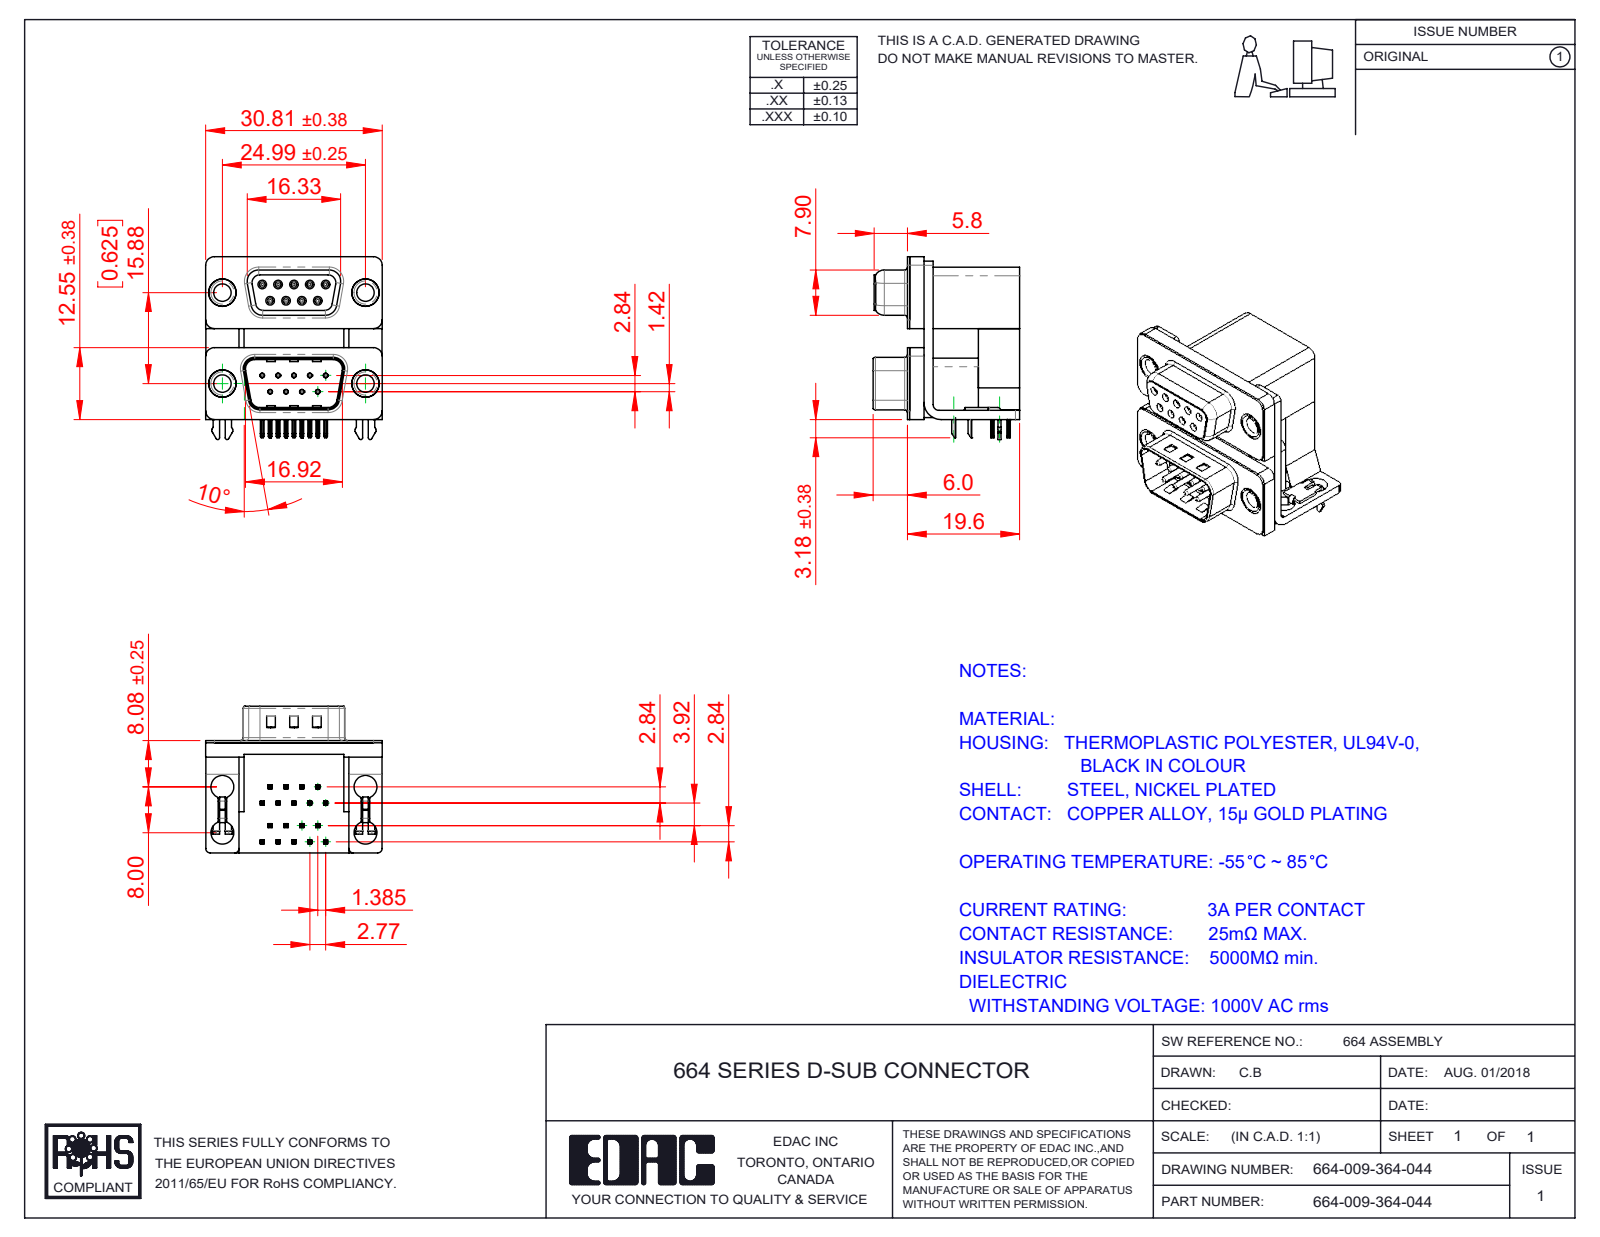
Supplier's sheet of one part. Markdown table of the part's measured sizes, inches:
| quantity | value |
| --- | --- |
| part name | 664 Shell Plug_09 Contacts; 664-009-364-044; 664 Housing Lower_09 Contacts; 664 Contact Bottom Upper_L (+8 more) |
| STEP written by | SolidWorks 2020 (CONFIG_CONTROL_DESIGN) |
| units | inches |
| bodies | 31 solids, 2553 faces (1341 planar, 689 cylindrical, 523 other) |
| overall size | 1.257 × 1.213 × 1.008 |
| volume | 0.628 in³ |
| surface area | 18.97 in² |
| round holes (diameter × count) | 0.031 × 18, 0.014 × 9, 0.035 × 9, 0.157 × 8, 0.12 × 4, 0.138 × 4, 0.189 × 4, 0.197 × 4 |
| round bosses / shafts (diameter × count) | 0.047 × 9, 0.03 × 9, 0.193 × 4, 0.187 × 4, 0.152 × 4 |
| partial cylindrical surfaces (radius × count) | 0.004 × 73, 0.01 × 42, 0.006 × 36, 0.005 × 18, 0.014 × 18, 0.02 × 16, 0.059 × 13, 0.03 × 10 |
| main face-to-face distances | 0.016, 0.098, 0.657, 0.756, 0.772, 0.114, 0.283, 0.374, 0.472, 0.488 |
| hole center spacings | 0.124, 0.109, 0.635, 0.625, 0.218, 0.662, 0.516, 0.739 |
